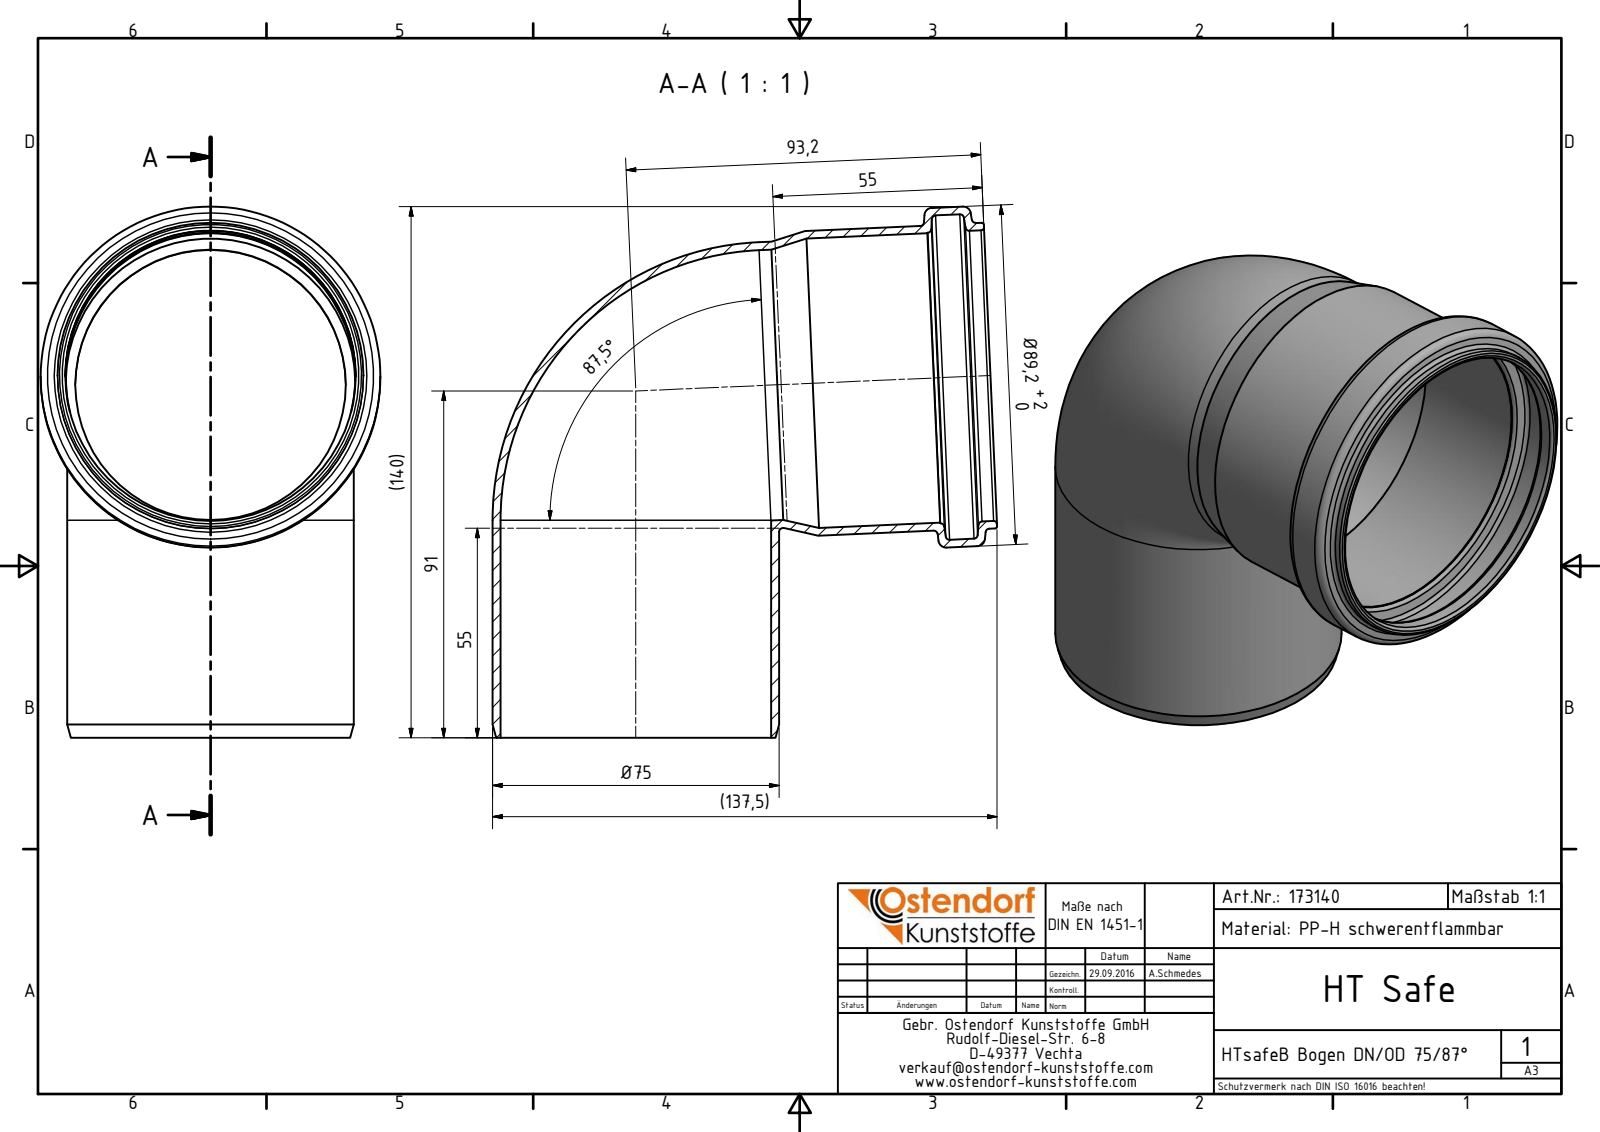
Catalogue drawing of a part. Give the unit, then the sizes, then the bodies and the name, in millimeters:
Units: millimetres
Overall size (bounding box): 139.39 × 132.44 × 89.2
Round holes (diameter × count): ⌀71 ×2, ⌀76 ×1, ⌀76.3 ×1, ⌀85.2 ×1
Round bosses / shafts (diameter × count): ⌀75.2 ×2, ⌀89.2 ×1, ⌀80.3 ×1, ⌀80 ×1
Main face-to-face distances: 14.89
Volume: 78 150 mm³ · Surface area: 84 665 mm²
Bodies: 1 solid, 34 faces (3 planar, 11 cylindrical, 20 other)
Part name (STEP PRODUCT): 173140 HTsafeB DN_OD 75_87°
STEP written by: Autodesk Inventor 2016 (AUTOMOTIVE_DESIGN)
